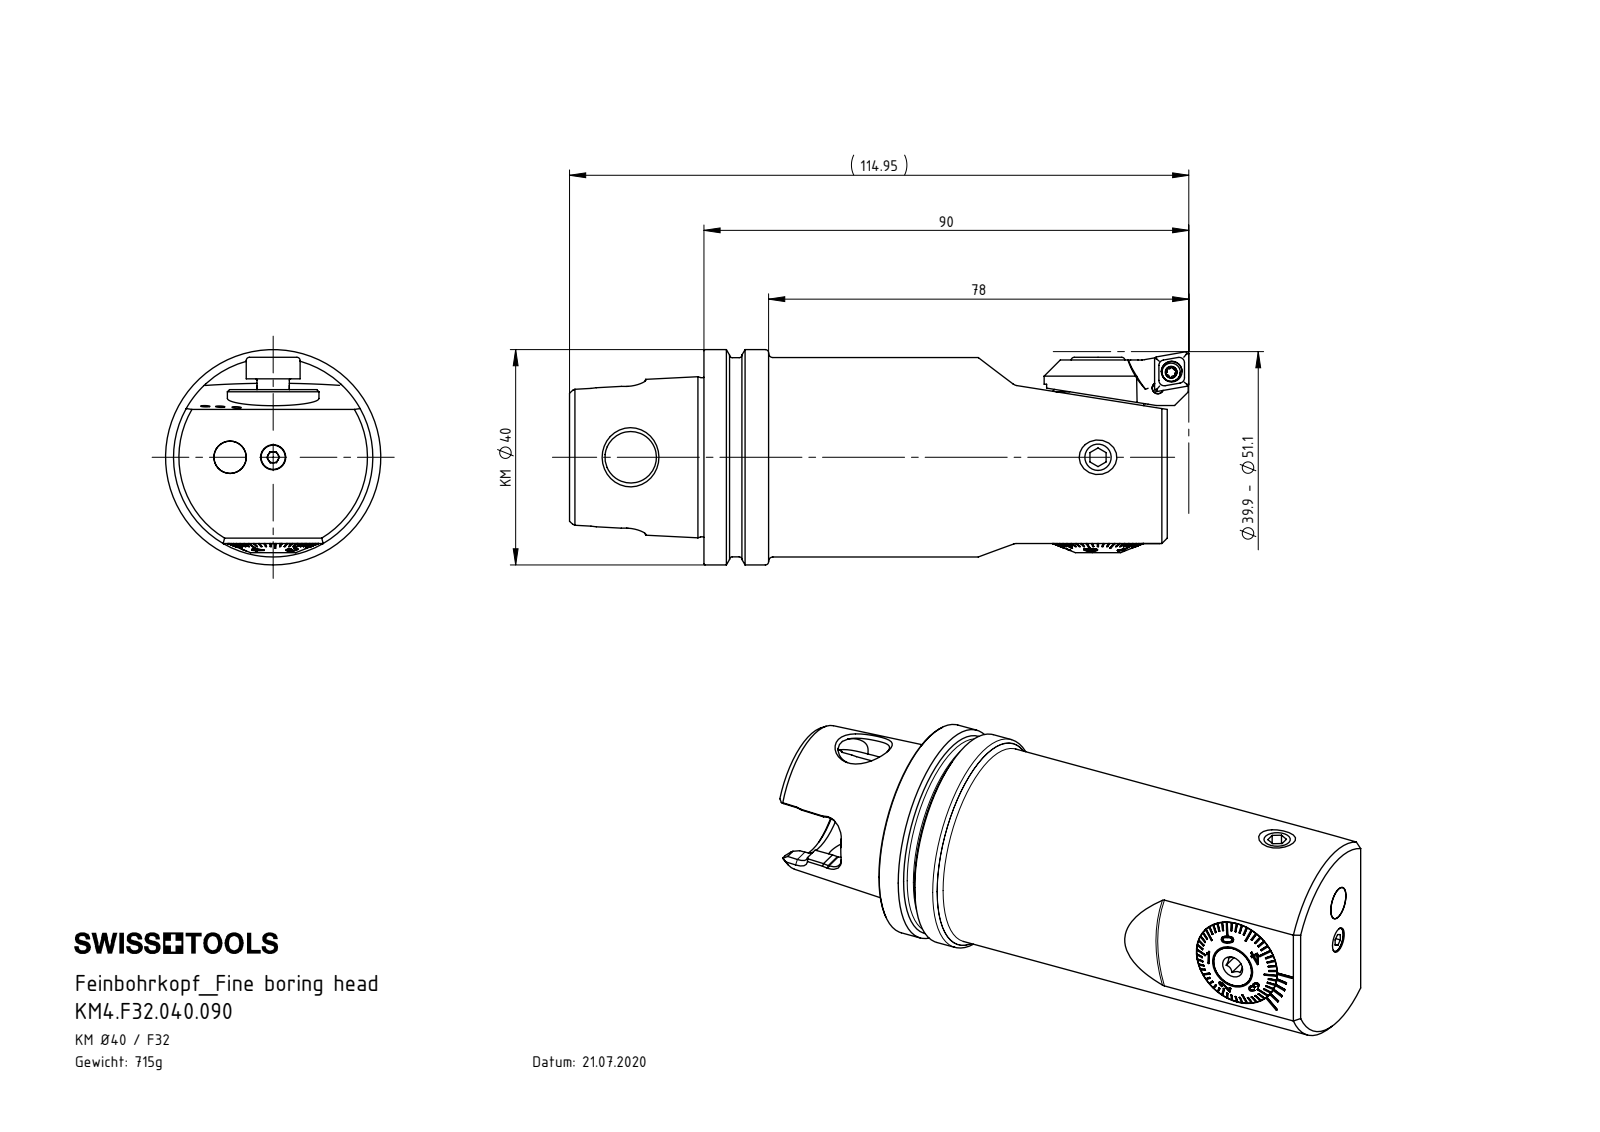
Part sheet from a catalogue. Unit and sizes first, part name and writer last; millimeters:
Units: millimetres
Overall size (bounding box): 110.95 × 39.95 × 39.95
Round holes (diameter × count): ⌀1.5 ×3, ⌀3.3 ×2, ⌀5 ×2, ⌀2.05 ×1, ⌀2.7 ×1, ⌀2.9 ×1, ⌀3 ×1, ⌀4.2 ×1, ⌀6 ×1, ⌀6.8 ×1, ⌀7 ×1, ⌀7.4 ×1
Round bosses / shafts (diameter × count): ⌀6 ×2, ⌀39.95 ×1, ⌀37 ×1, ⌀36.95 ×1, ⌀17 ×1, ⌀16.98 ×1, ⌀16.85 ×1, ⌀14.65 ×1
Partial cylindrical surfaces — rounded edges, fillets, slot ends (radius × count): R3.1 ×6, R1.4 ×4, R0.5 ×3, R1.75 ×2, R2 ×2, R4.54 ×2, R2.1 ×1, R3.2 ×1
Main face-to-face distances: 86, 4.5, 0.8, 3.7, 1.5, 0.5, 85.5, 24.05, 2.2, 2.3
Hole centre spacings: 8, 8.72, 86.75, 93.76
Volume: 91 706 mm³ · Surface area: 25 400 mm²
Bodies: 14 solids, 614 faces (331 planar, 82 cylindrical, 201 other)
Part name (STEP PRODUCT): F32-BG2.017.003_A; F32-BG2.014.012_A; F32-BG1.DA3.017_B_Aktuell 0.6.2014-Mx1.3; KM4.F32.AA4.090 (+8 more)
STEP written by: SolidWorks 2017 (AUTOMOTIVE_DESIGN)
